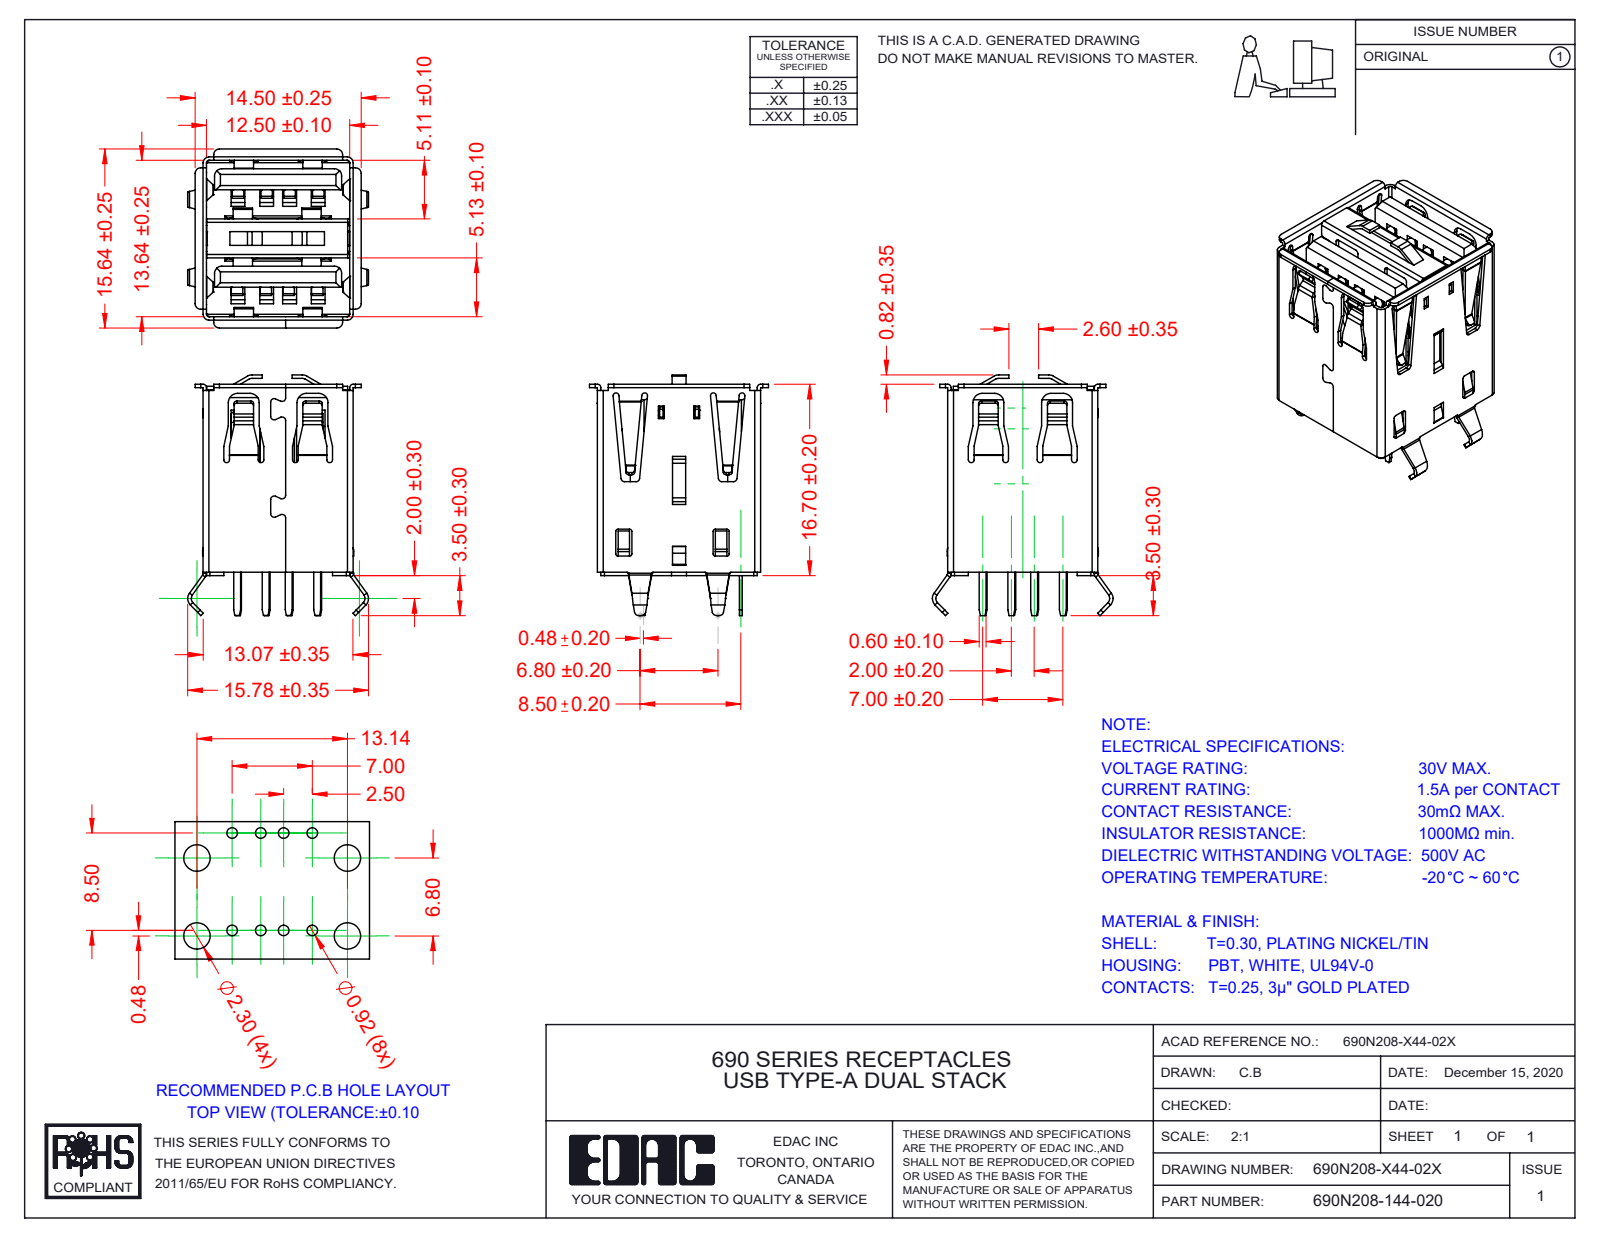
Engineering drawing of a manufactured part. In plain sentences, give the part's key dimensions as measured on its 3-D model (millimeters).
The part is named "Contact 6 690N208-X44-02X; 690N208-144-020; Contact Lock Lower 690N208-X44-02X_Black; Contact 4 690N208-X44-02X (+8 more)". Its 3-D file was written by "SolidWorks 2020 (AUTOMOTIVE_DESIGN)". It is 13 solids with 1538 faces: 1164 planar, 342 cylindrical and 32 other. Overall it measures 21.02 by 15.78 by 15.64 millimeters. Its volume is 1 797 cubic millimeters and its surface area 5 240 square millimeters. Partial cylindrical surfaces (rounded edges, fillets, slot ends): 48 of radius 0.3, 40 of radius 0.25, 24 of radius 0.5, 22 of radius 0.1, 20 of radius 0.2, 8 of radius 0.45, 8 of radius 0.62, 8 of radius 0.8. The main face-to-face distances are 12.8, 13.94, 5.8, 12.5, 8.14, 8.44, 5.5, 13.64, 8.5, 2.5.
